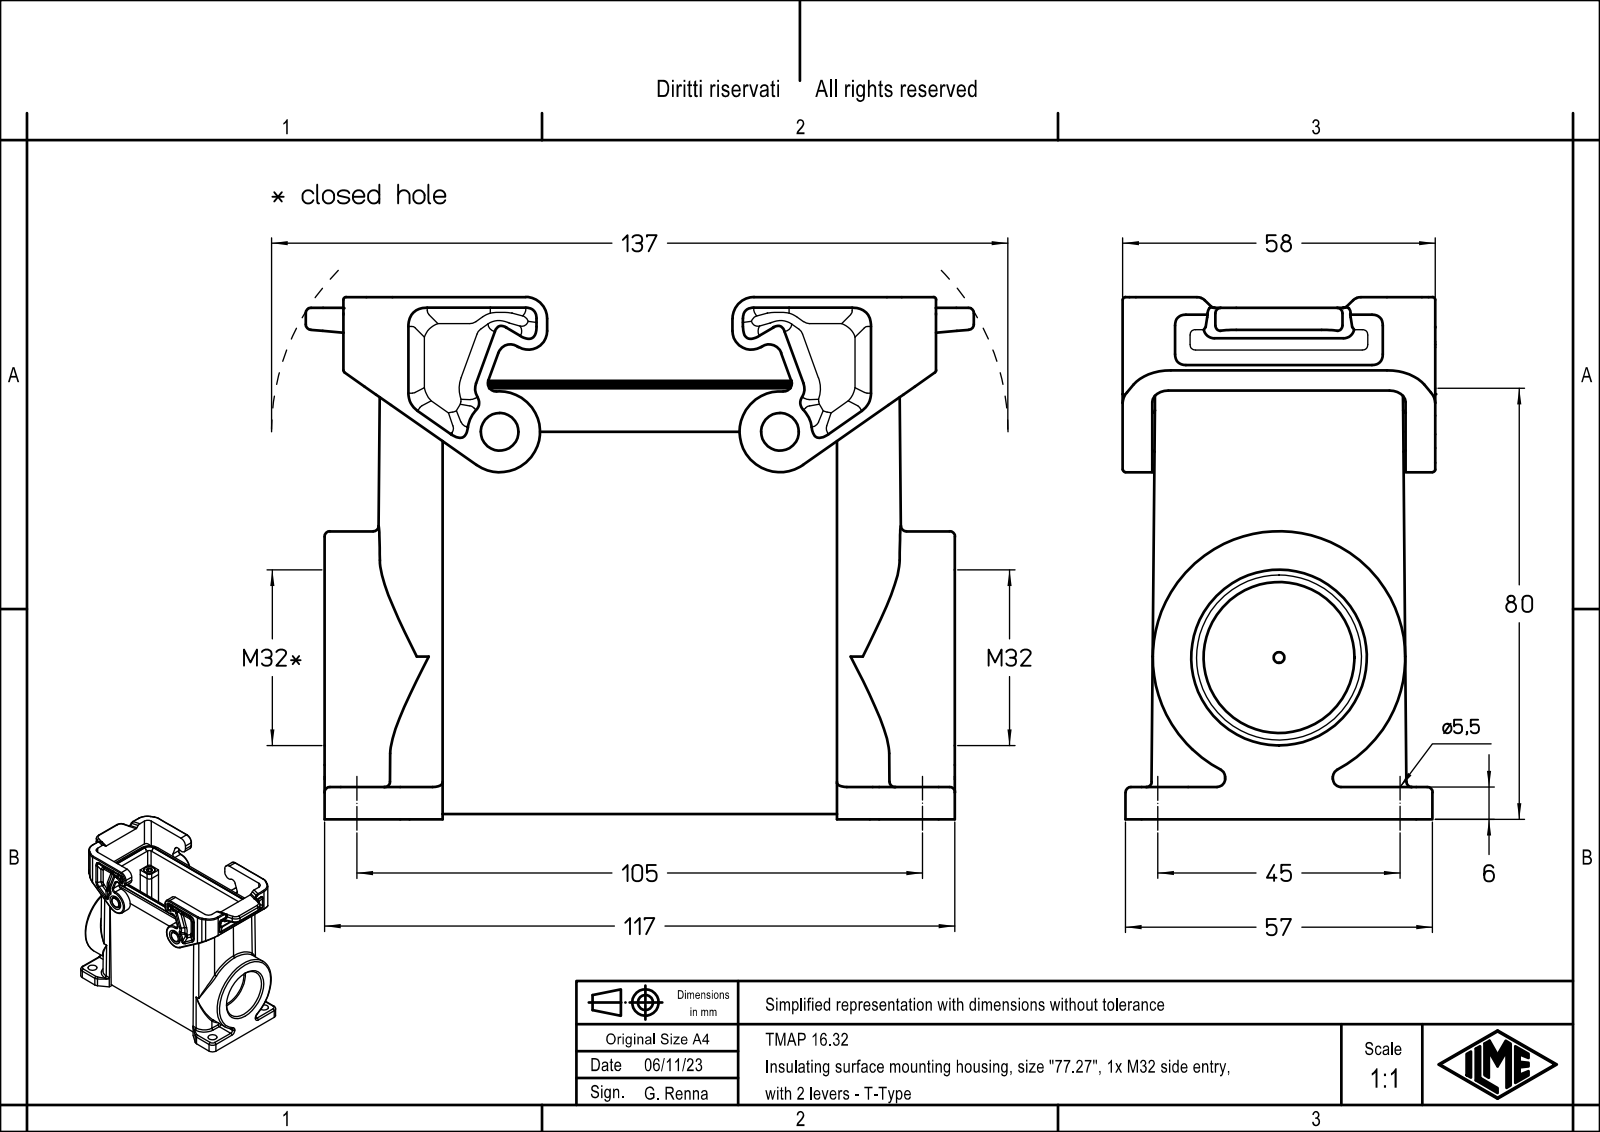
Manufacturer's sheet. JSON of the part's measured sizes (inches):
{"part_name": "TMAP 16.32", "step_written_by": "Creo Elements/Direct Modeling 20.1B 02-Apr-2019 (C) Parametric Technology GmbH (AUTOMOTIVE_DESIGN)", "units": "inches", "bodies": {"solids": 1, "faces": 418, "planar": 208, "cylindrical": 158, "other": 52}, "overall_size": [4.882, 3.815, 2.283], "volume_in3": 12.1, "surface_area_in2": 108.1, "round_holes": [[0.217, 4], [1.102, 1], [1.205, 1]], "round_bosses_or_shafts": [[0.276, 2], [1.845, 1]], "partial_cylinders_radius": [[0.118, 20], [0.039, 16], [0.079, 16], [0.059, 10], [0.051, 8], [0.236, 8], [0.276, 8], [0.157, 6]], "face_to_face_distances": [1.386, 0.217, 0.232, 1.618, 0.256, 0.039, 0.449, 1.835, 2.067, 0.197], "hole_center_spacings": [1.772, 4.134, 4.498]}
